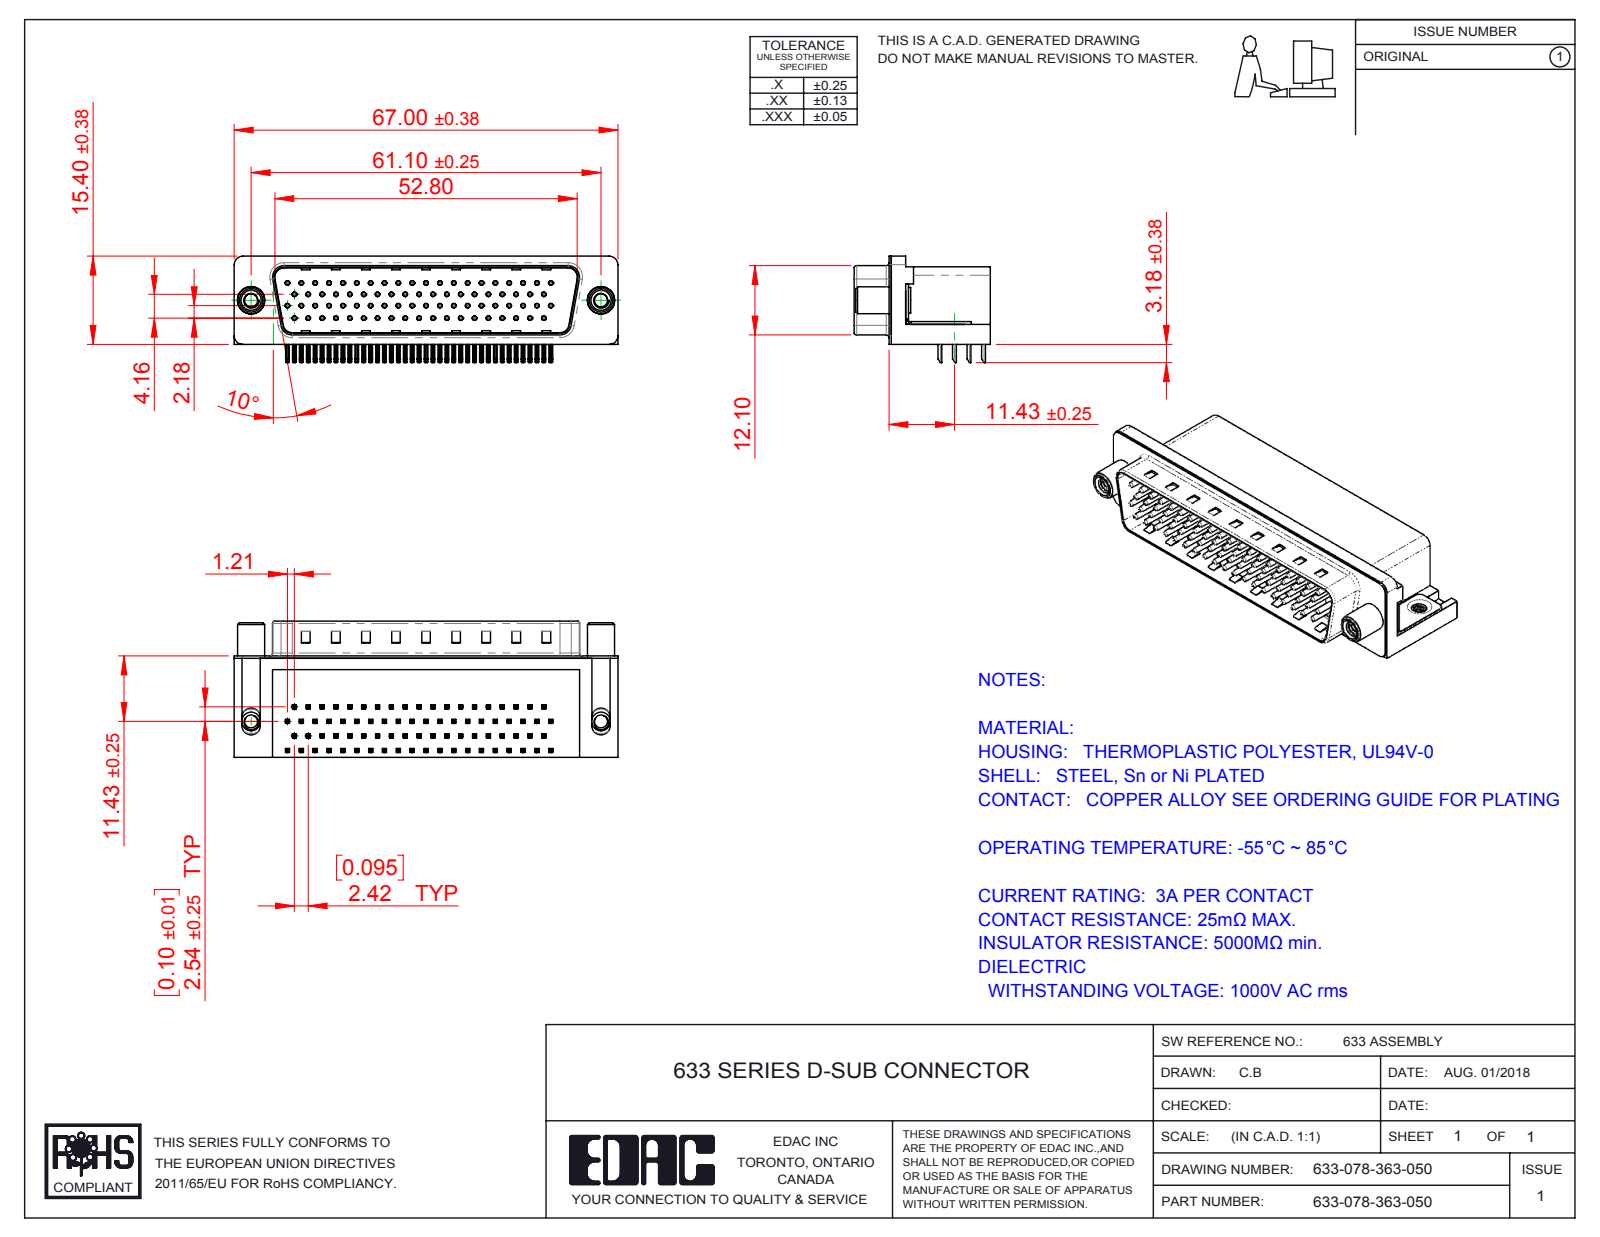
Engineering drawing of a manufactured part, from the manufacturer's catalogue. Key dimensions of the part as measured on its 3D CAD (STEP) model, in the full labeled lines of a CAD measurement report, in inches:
Part name (STEP PRODUCT): 633 Shell_78 Contact; 633 Contact Middle_78 Contact; 633-078-363-050; 633 4-40 Threaded Board Mount_78 Contact (+5 more)
STEP written by: SolidWorks 2016 (CONFIG_CONTROL_DESIGN)
Units: inches
Bodies: 84 solids, 6300 faces (3973 planar, 1798 cylindrical, 529 other)
Overall size (bounding box): 2.638 × 0.937 × 0.731
Volume: 0.898 in³ · Surface area: 25.77 in²
Round holes (diameter × count): ⌀0.014 ×78, ⌀0.031 ×78, ⌀0.089 ×2, ⌀0.091 ×2, ⌀0.122 ×2, ⌀0.157 ×2, ⌀0.189 ×2, ⌀0.197 ×2
Round bosses / shafts (diameter × count): ⌀0.03 ×78, ⌀0.193 ×2, ⌀0.185 ×2, ⌀0.177 ×2, ⌀0.152 ×2, ⌀0.128 ×2
Partial cylindrical surfaces — rounded edges, fillets, slot ends (radius × count): R0.01 ×312, R0.005 ×156, R0.039 ×16, R0.02 ×9, R0.063 ×8, R0.059 ×6, R0.018 ×4, R0.035 ×4
Main face-to-face distances: 0.016, 0.52, 0.681, 0.461, 0.526, 0.081, 0.541, 0.065, 0.073, 0.469
Hole centre spacings: 0.095, 0.191, 0.286, 0.381, 0.246, 0.281, 0.476, 0.339
